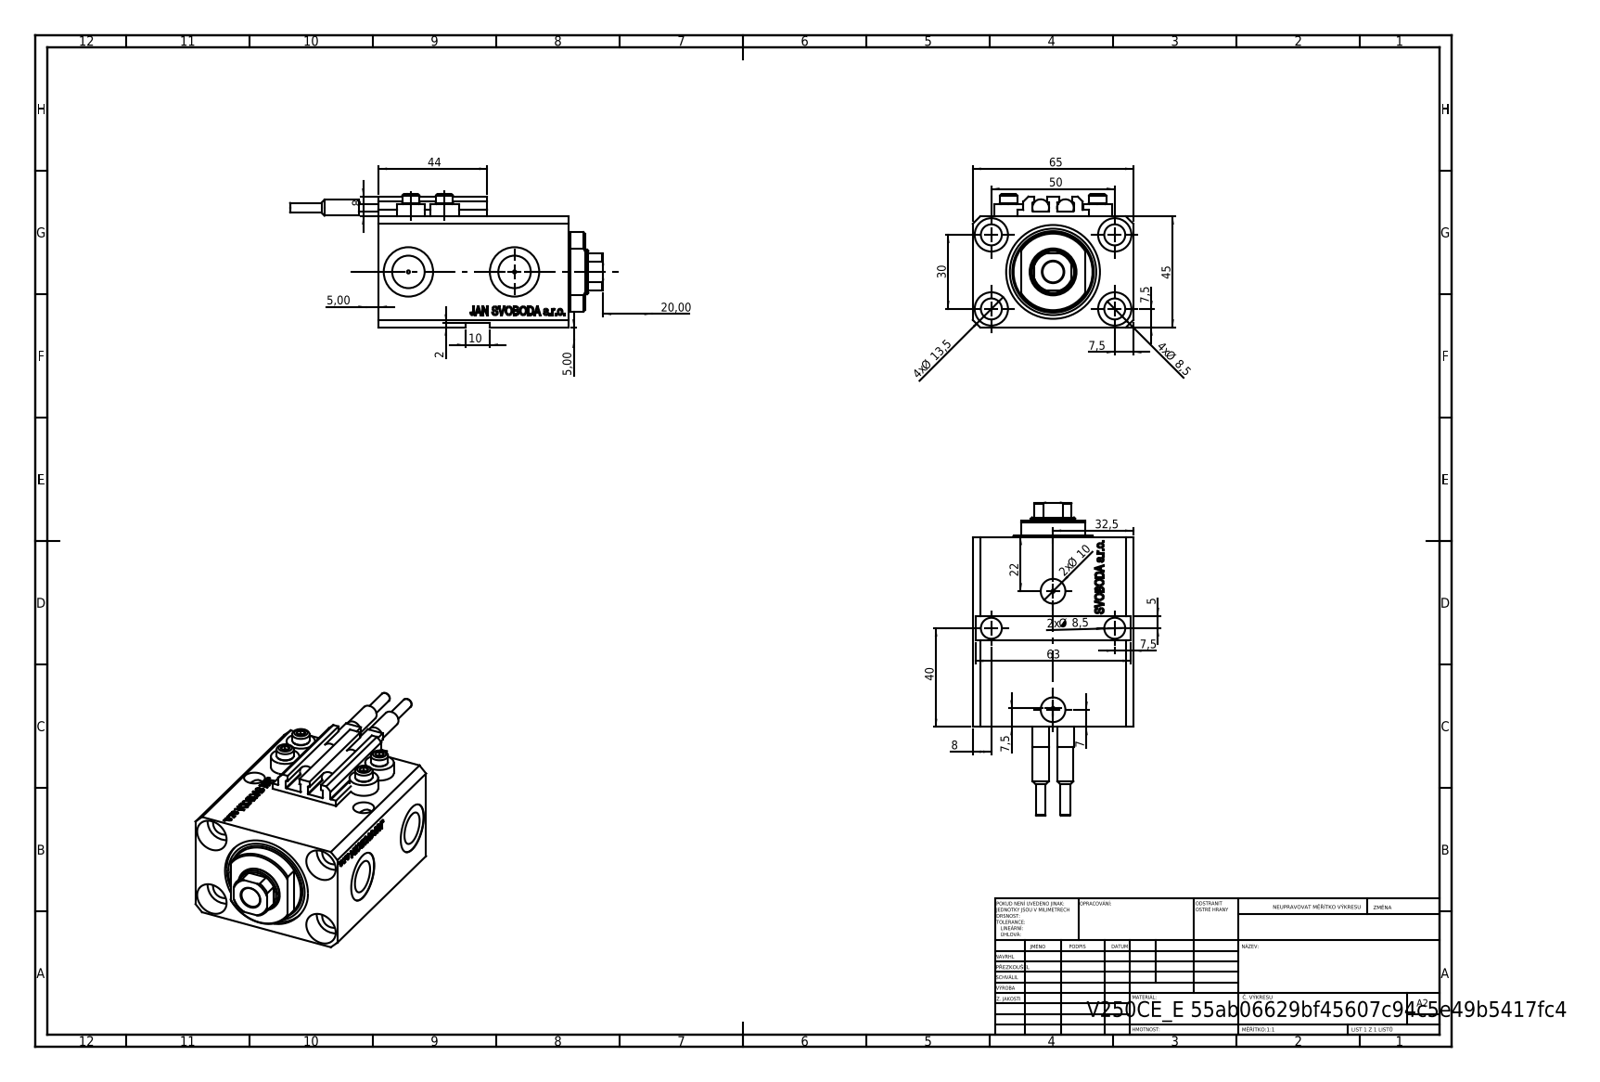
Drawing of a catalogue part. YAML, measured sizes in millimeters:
part_name: "V250CE_C_VCP; ALLEN BOLT V250CE; V250CE_E_Body; V250CE_VC_E (+1 more)"
step_written_by: "SolidWorks 2019 (CONFIG_CONTROL_DESIGN)"
units: millimeters
bodies: {solids: 10, faces: 1135, planar: 547, cylindrical: 150, other: 438}
overall_size: [126.9, 65, 54]
volume: 199730
surface_area: 65152
round_holes:
  - {diameter: 8.5, count: 7}
  - {diameter: 1.25, count: 4}
  - {diameter: 4, count: 4}
  - {diameter: 13.5, count: 4}
  - {diameter: 10, count: 2}
  - {diameter: 13.16, count: 2}
  - {diameter: 20, count: 2}
  - {diameter: 18, count: 1}
  - {diameter: 25, count: 1}
  - {diameter: 38, count: 1}
round_bosses_or_shafts:
  - {diameter: 11.6, count: 4}
  - {diameter: 7, count: 4}
  - {diameter: 6.8, count: 2}
  - {diameter: 6.5, count: 2}
  - {diameter: 4, count: 2}
partial_cylinders:
  - {radius: 0.2, count: 10}
  - {radius: 8.5, count: 1}
  - {radius: 16, count: 1}
face_to_face_distances: [45, 65, 51.9, 2, 25.1, 3, 77, 6.9, 47, 70.1]
hole_center_spacings: [29.15, 50, 13.6, 15.12, 18.81, 18.97, 26.22, 26.61]
